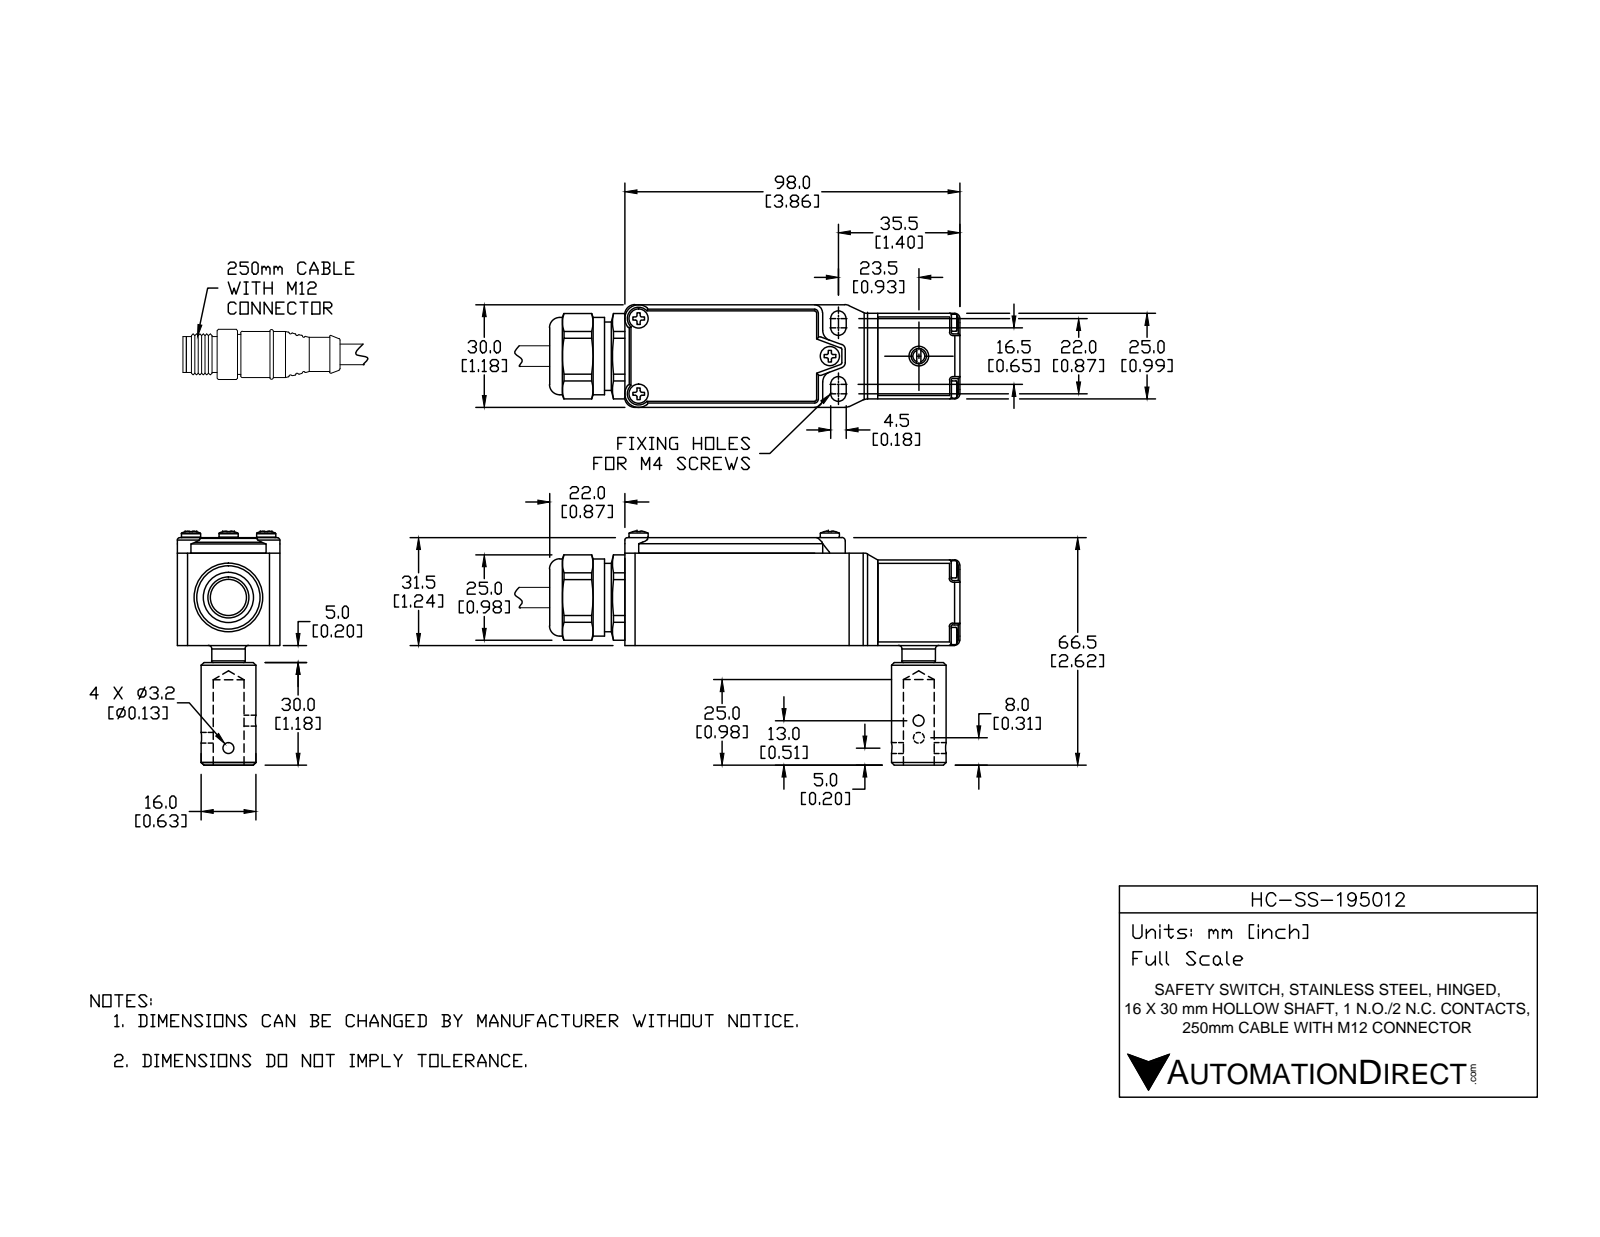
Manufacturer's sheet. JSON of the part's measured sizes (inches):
{"part_name": "HC-SS-195012", "step_written_by": "SolidWorks 2014 (AUTOMOTIVE_DESIGN)", "units": "inches", "bodies": {"solids": 13, "faces": 1182, "planar": 347, "cylindrical": 476, "other": 359}, "overall_size": [3.898, 2.694, 1.181], "volume_in3": 2.656, "surface_area_in2": 54.51, "round_holes": [[0.126, 10], [0.098, 8], [0.157, 3], [0.059, 2], [0.071, 2], [0.087, 2], [0.142, 2], [0.081, 1], [0.114, 1], [0.173, 1], [0.185, 1], [0.217, 1]], "round_bosses_or_shafts": [[0.118, 7], [0.197, 5], [0.138, 4], [0.22, 3], [0.925, 1], [0.697, 1], [0.63, 1], [0.386, 1]], "partial_cylinders_radius": [[0.02, 175], [0.039, 20], [0.012, 18], [0.006, 14], [0.028, 8], [0.118, 8], [0.059, 6], [0.089, 4]], "face_to_face_distances": [0.098, 1.142, 0.079, 1.181, 0.114, 1.067, 0.177, 1.24, 0.016, 1.043], "hole_center_spacings": [0.543, 0.768, 0.187, 0.245, 0.414, 0.423, 0.426, 0.476]}
